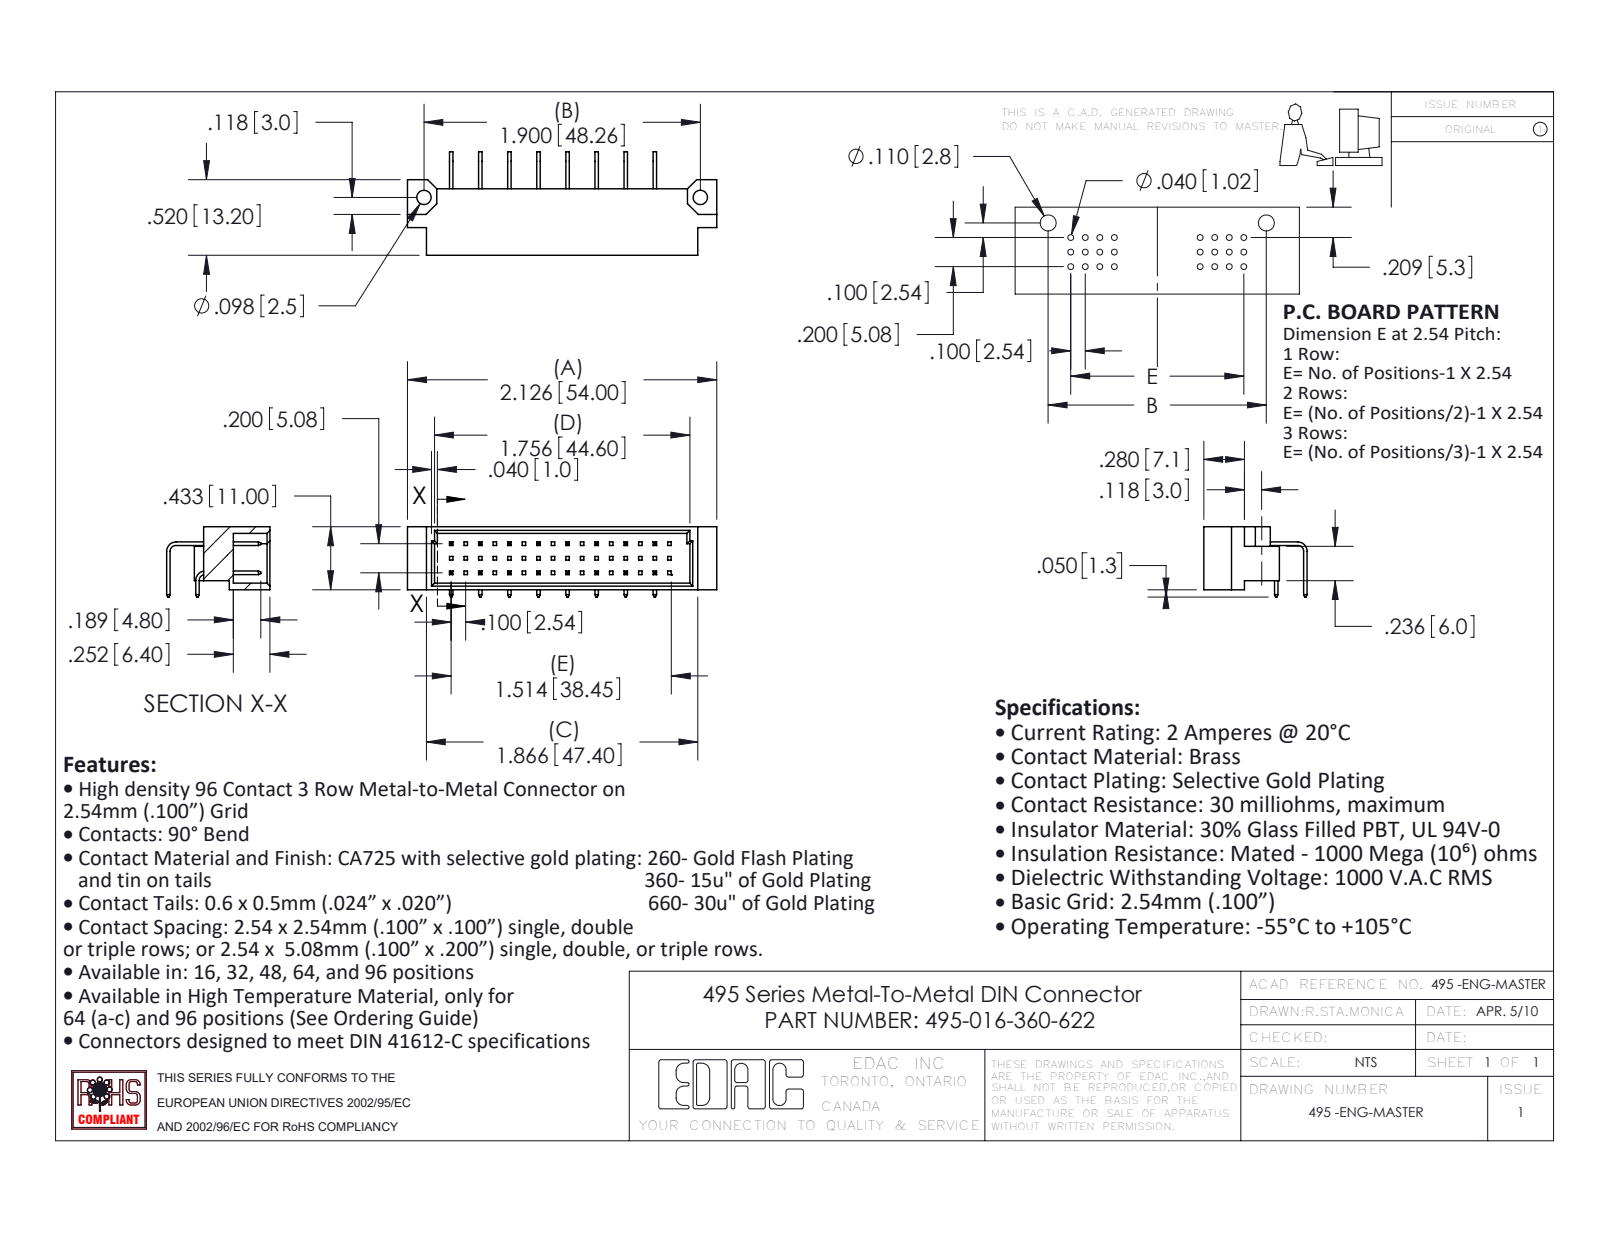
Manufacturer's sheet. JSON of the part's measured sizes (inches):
{"part_name": "495 Part_48; 495-016-360-622; 495-290-1; 495-290-3", "step_written_by": "SolidWorks 2020 (AUTOMOTIVE_DESIGN)", "units": "inches", "bodies": {"solids": 17, "faces": 530, "planar": 494, "cylindrical": 36, "other": 0}, "overall_size": [2.126, 0.711, 0.483], "volume_in3": 0.218, "surface_area_in2": 7.33, "round_holes": [[0.098, 2]], "partial_cylinders_radius": [[0.04, 2], [0.065, 2]], "face_to_face_distances": [0.2, 0.045, 0.388, 0.205, 0.433, 0.024, 0.6, 0.063, 0.4, 0.343], "hole_center_spacings": [1.9]}
